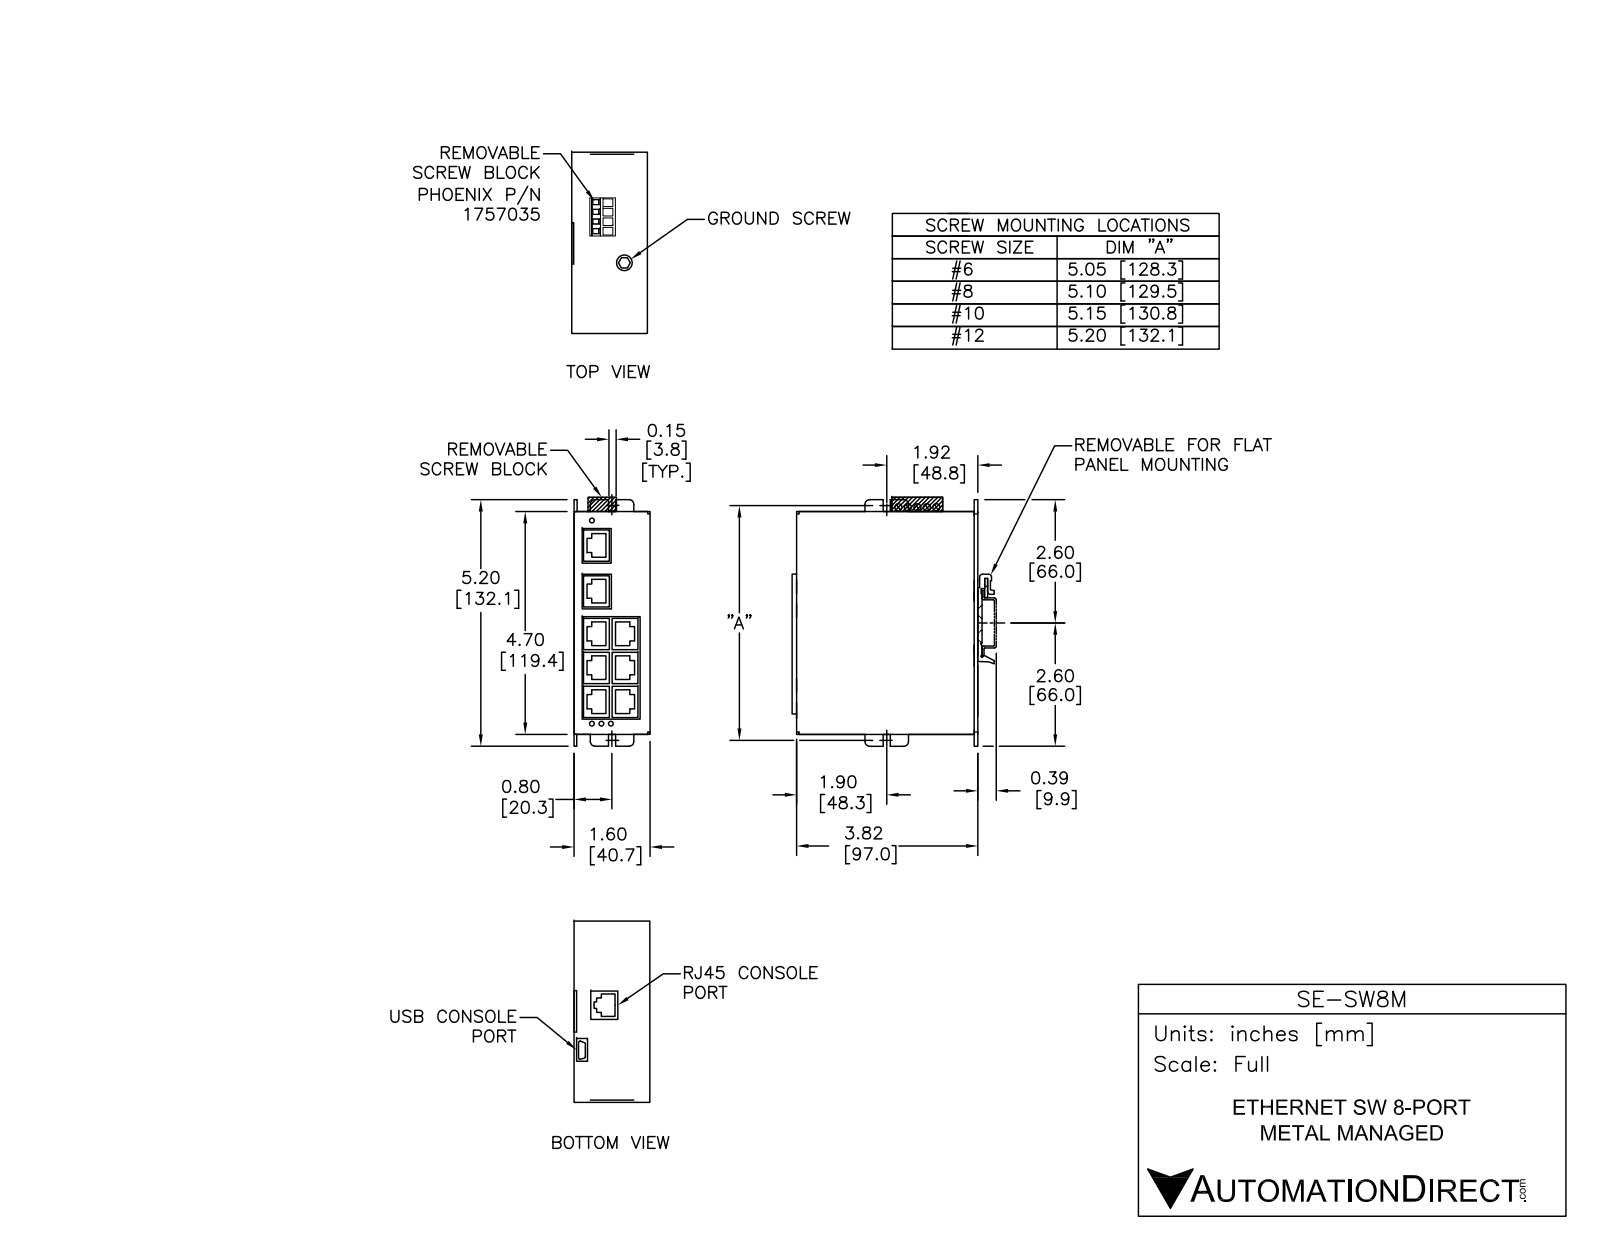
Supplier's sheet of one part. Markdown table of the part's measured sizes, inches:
| quantity | value |
| --- | --- |
| part name | SE-SW8M |
| STEP written by | SolidWorks 2017 (AUTOMOTIVE_DESIGN) |
| units | inches |
| bodies | 3 solids, 486 faces (436 planar, 50 cylindrical, 0 other) |
| overall size | 5.38 × 4.239 × 1.6 |
| volume | 28.94 in³ |
| surface area | 132.5 in² |
| round holes (diameter × count) | 0.11 × 6, 0.159 × 4, 0.216 × 1 |
| round bosses / shafts (diameter × count) | 0.33 × 1 |
| partial cylindrical surfaces (radius × count) | 0.1 × 8, 0.03 × 6, 0.015 × 4, 0.06 × 4, 0.07 × 4, 0.017 × 2, 0.032 × 2, 0.045 × 2 |
| main face-to-face distances | 0.059, 1.6, 0.06, 1.54, 1.541, 4.7, 0.06, 3.82, 3.761, 3.76 |
| hole center spacings | 0.185, 4.372, 0.257, 0.272, 0.37, 0.529, 4.379, 4.38 |
